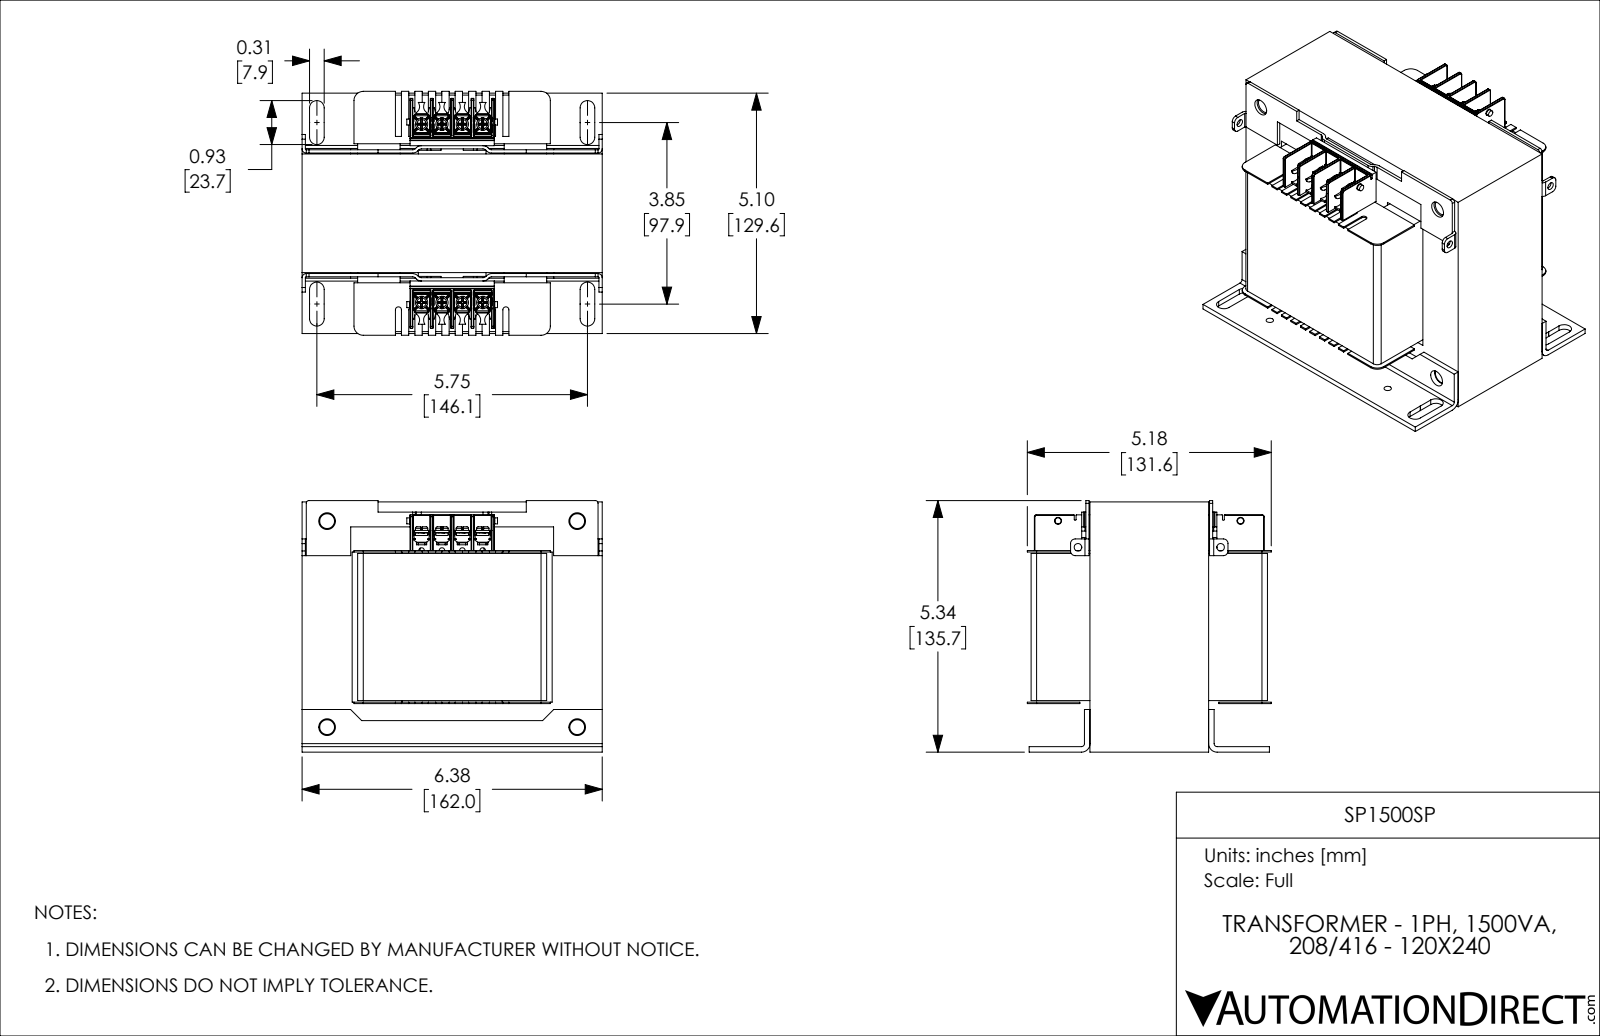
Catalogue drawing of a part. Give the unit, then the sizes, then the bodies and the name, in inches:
Units: inches
Overall size (bounding box): 6.378 × 5.344 × 5.181
Round holes (diameter × count): ⌀0.105 ×8, ⌀0.138 ×8, ⌀0.157 ×4, ⌀0.315 ×4, ⌀0.354 ×4, ⌀0.161 ×2
Round bosses / shafts (diameter × count): ⌀0.262 ×8, ⌀0.168 ×8, ⌀0.11 ×8, ⌀0.128 ×2
Partial cylindrical surfaces — rounded edges, fillets, slot ends (radius × count): R0.005 ×52, R0.01 ×52, R0.012 ×36, R0.029 ×32, R0.157 ×16, R0.035 ×12, R0.156 ×8, R0.02 ×6
Main face-to-face distances: 1.063, 5.197, 0.118, 4.252, 5.315, 2.52, 1.181, 1.094, 4.22, 3.189
Hole centre spacings: 0.433, 3.812, 0.866, 1.124, 1.557, 1.989, 2.422, 3.787
Volume: 115.2 in³ · Surface area: 424.2 in²
Bodies: 36 solids, 3056 faces (1878 planar, 872 cylindrical, 306 other)
Part name (STEP PRODUCT): SP1500SP
STEP written by: SolidWorks 2018 (AUTOMOTIVE_DESIGN)
